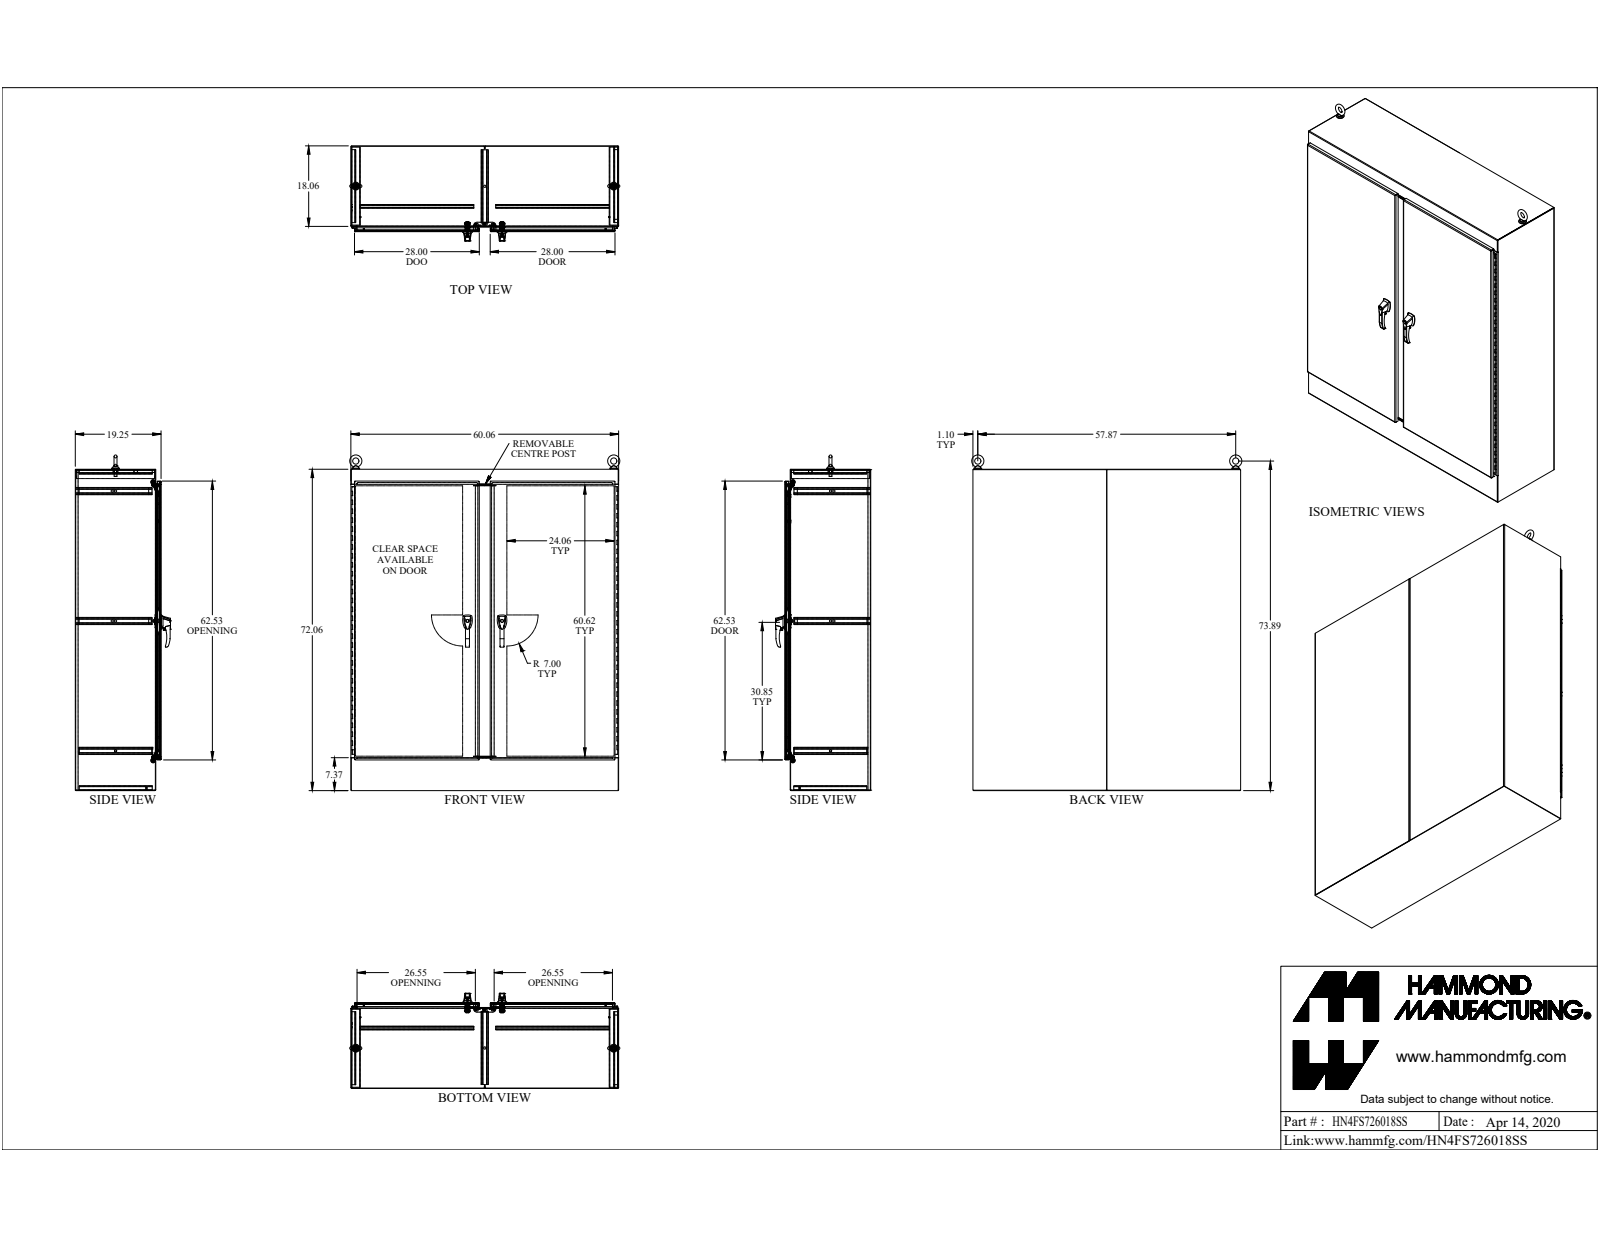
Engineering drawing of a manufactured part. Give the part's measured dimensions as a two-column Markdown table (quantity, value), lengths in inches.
| quantity | value |
| --- | --- |
| part name | HN4FS726018SS |
| STEP written by | SolidWorks 2019 (CONFIG_CONTROL_DESIGN) |
| units | inches |
| bodies | 104 solids, 2931 faces (1543 planar, 1142 cylindrical, 246 other) |
| overall size | 75.256 × 60.604 × 21.362 |
| volume | 1 561 in³ |
| surface area | 32 966 in² |
| round holes (diameter × count) | 0.304 × 20, 0.35 × 8, 0.5 × 7, 0.25 × 4, 0.257 × 4, 0.28 × 4, 0.281 × 4, 0.313 × 4, 0.39 × 4, 0.413 × 4, 0.201 × 3, 0.313 × 3 |
| round bosses / shafts (diameter × count) | 1 × 4, 0.75 × 4, 0.63 × 4, 0.625 × 4, 0.44 × 4, 0.37 × 4, 0.313 × 4, 0.281 × 4 |
| partial cylindrical surfaces (radius × count) | 0.043 × 54, 0.138 × 48, 0.5 × 33, 0.1 × 28, 0.125 × 27, 0.06 × 24, 0.318 × 19, 0.017 × 16 |
| main face-to-face distances | 0.095, 19.152, 19.057, 19.247, 59.965, 71.965, 1.187, 17.965, 59.87, 60.06 |
| hole center spacings | 6, 58.636, 12, 59.55, 18, 61.043, 24, 63.073 |
